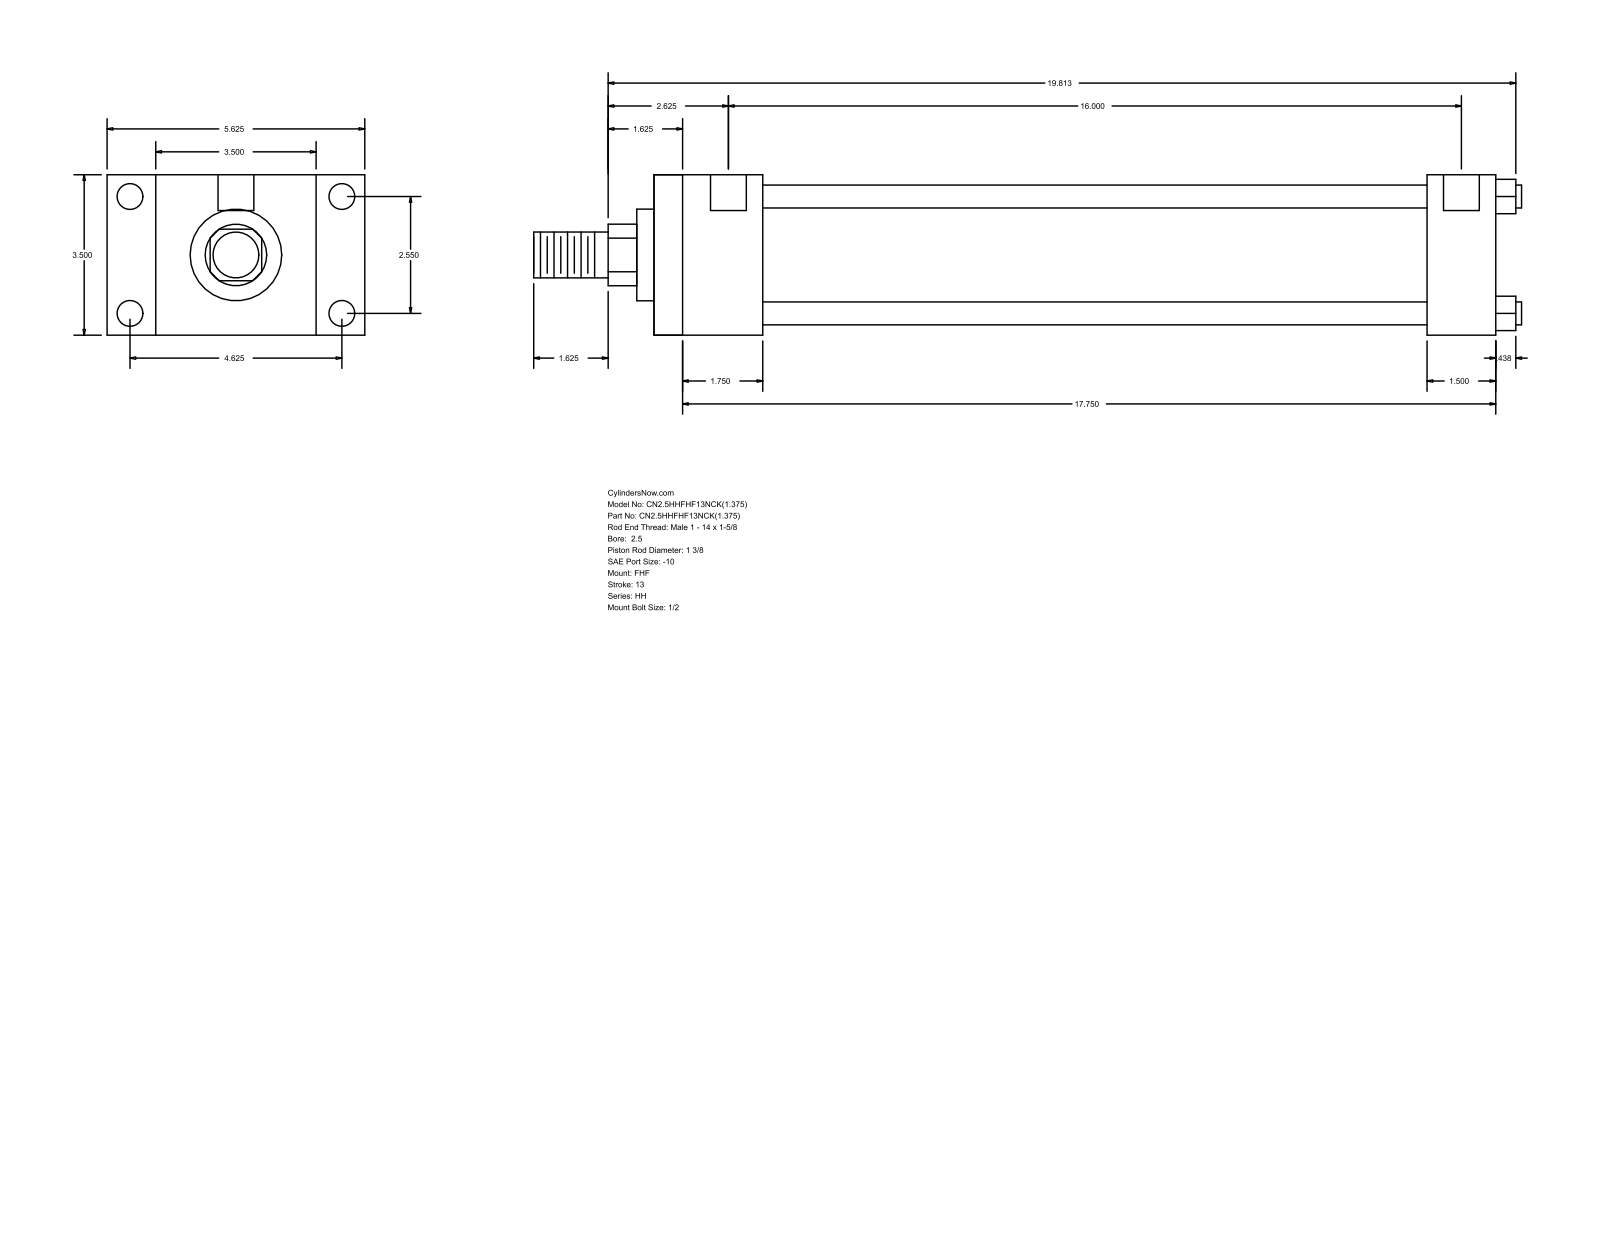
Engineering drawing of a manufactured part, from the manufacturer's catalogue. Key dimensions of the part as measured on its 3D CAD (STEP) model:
Part name (STEP PRODUCT): HH_FHF__0250_1.375
STEP written by: GSSL Pune (CONFIG_CONTROL_DESIGN)
Units: millimetres
Bodies: 0 solids, 88 faces (60 planar, 28 cylindrical, 0 other)
Overall size (bounding box): 547.69 × 142.88 × 88.9
Round holes (diameter × count): ⌀5.56 ×4, ⌀14.3 ×4, ⌀19.84 ×2
Round bosses / shafts (diameter × count): ⌀12.7 ×4, ⌀73.03 ×1, ⌀50.8 ×1, ⌀34.92 ×1, ⌀25.4 ×1
Partial cylindrical surfaces — rounded edges, fillets, slot ends (radius × count): R17.06 ×1
Main face-to-face distances: 88.9, 60.32, 26.99, 115.89, 466.72, 406.4, 142.88, 428.62, 368.3, 38.1
Hole centre spacings: 64.76, 117.48, 134.15, 409.57, 1.58, 1.59, 406.4, 407.98
